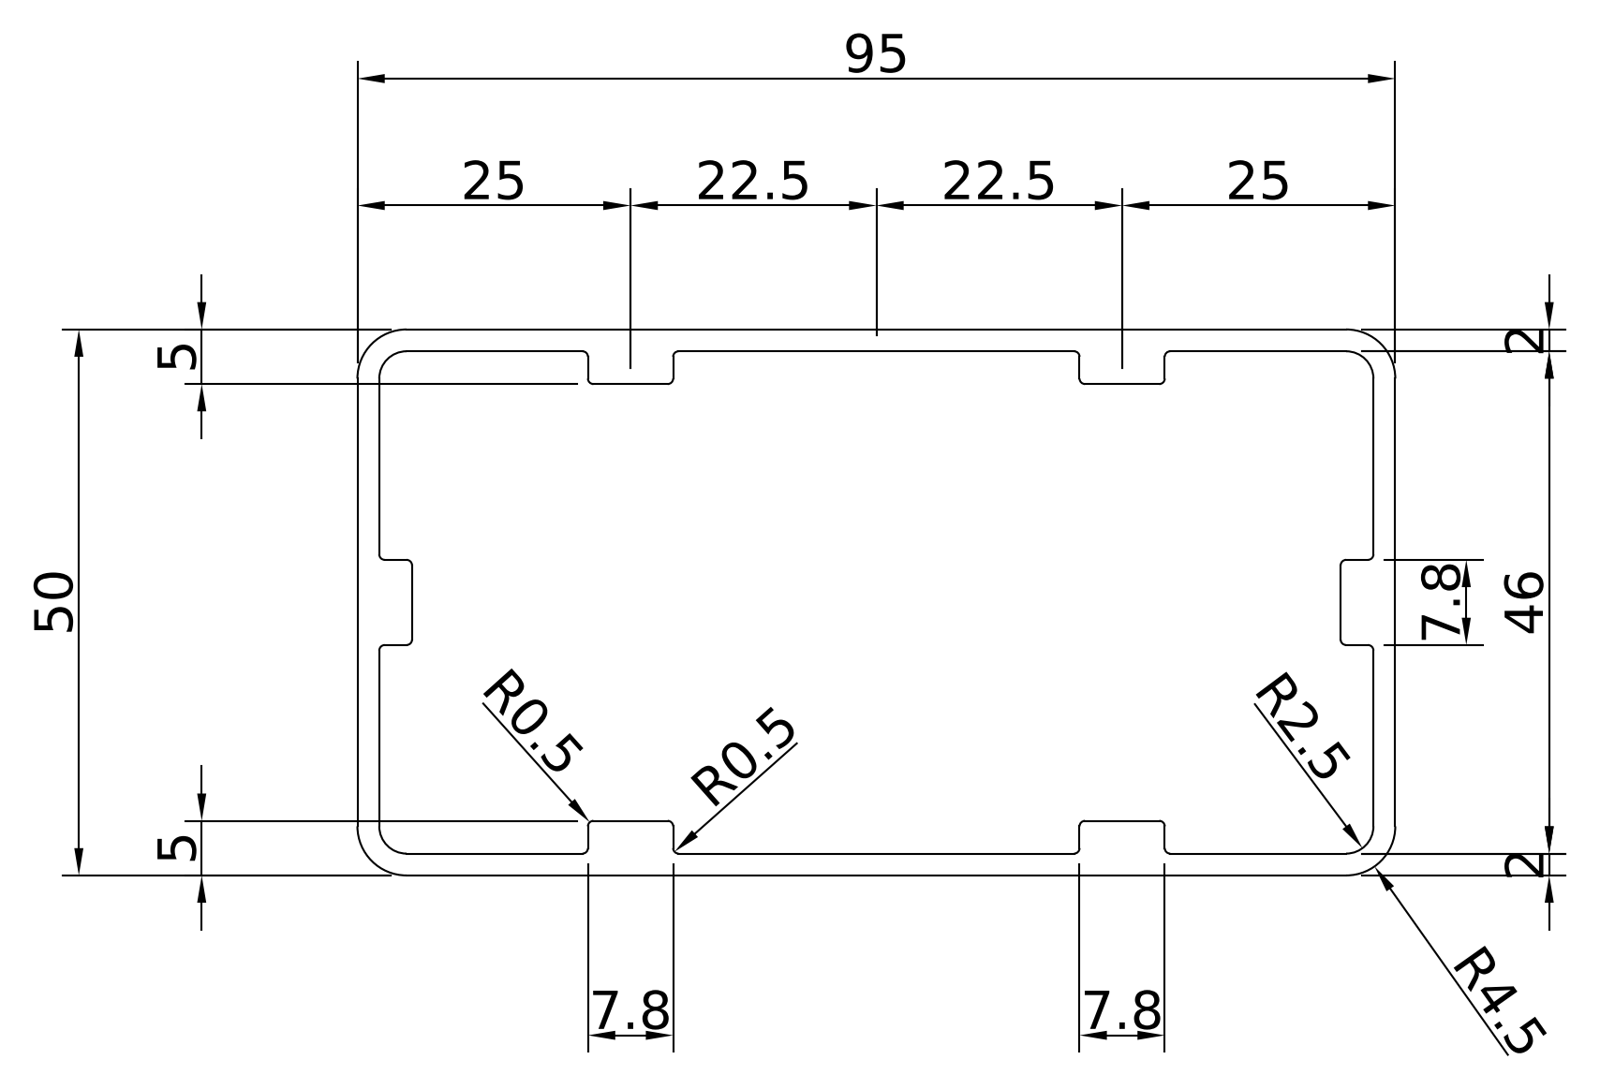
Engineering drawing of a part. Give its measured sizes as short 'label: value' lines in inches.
name: BPRRR0000057
written by: Autodesk Inventor 2019 (AUTOMOTIVE_DESIGN)
unit: in
bodies: 1 solid, 66 faces (34 planar, 32 cylindrical, 0 other)
size: 3.937 × 3.74 × 1.969
volume: 4.225 in³; area: 92.49 in²
rounds: 24× R0.02, 4× R0.098, 4× R0.177
face distances: 0.079, 1.89, 1.969, 1.811, 3.661, 3.74, 0.197, 0.118, 1.772, 3.583
